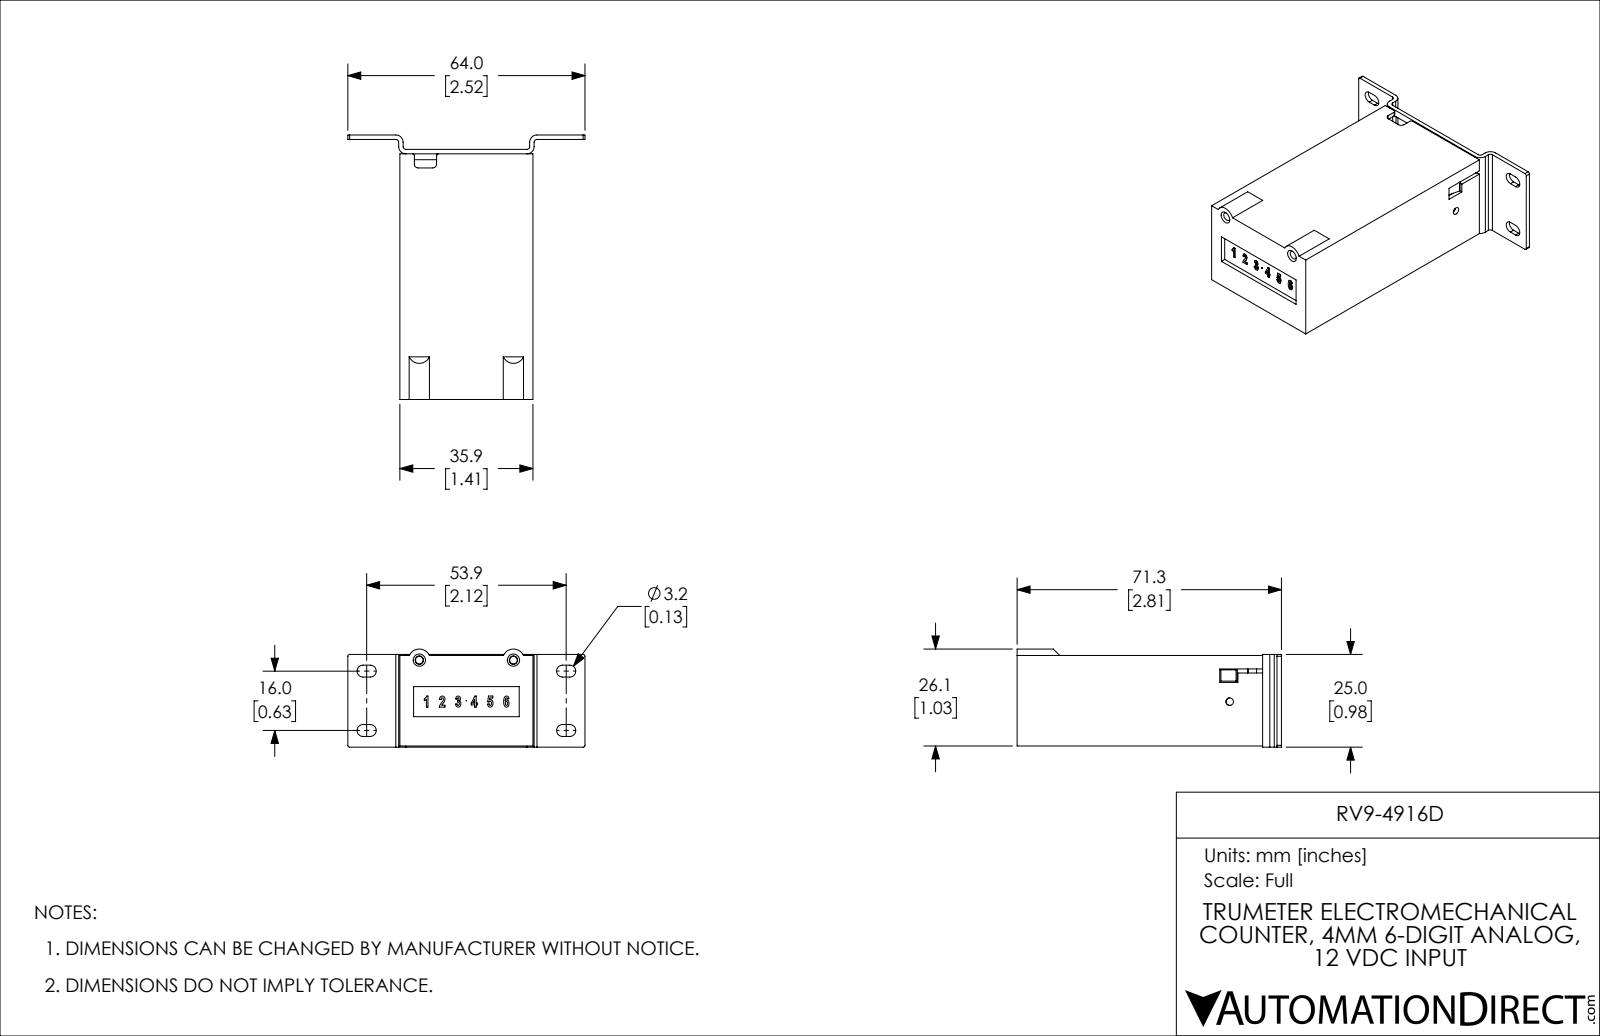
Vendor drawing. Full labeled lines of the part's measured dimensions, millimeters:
Part name (STEP PRODUCT): RV9-4916D
STEP written by: SolidWorks 2021 (CONFIG_CONTROL_DESIGN)
Units: millimetres
Bodies: 1 solid, 354 faces (219 planar, 104 cylindrical, 31 other)
Overall size (bounding box): 71.33 × 64 × 26.46
Volume: 18 281 mm³ · Surface area: 26 612 mm²
Round holes (diameter × count): ⌀2.02 ×5, ⌀3.17 ×2, ⌀4 ×2, ⌀2.01 ×1, ⌀2.03 ×1, ⌀2.46 ×1, ⌀2.46 ×1, ⌀3.12 ×1, ⌀5.6 ×1
Round bosses / shafts (diameter × count): ⌀6 ×2
Partial cylindrical surfaces — rounded edges, fillets, slot ends (radius × count): R0.5 ×11, R1 ×10, R1.6 ×8, R0.75 ×4, R1.95 ×4, R0.25 ×2, R0.3 ×2, R1.5 ×2
Main face-to-face distances: 1.6, 1.35, 34.55, 2.95, 32.95, 31.6, 24.39, 35.9, 33.2, 30
Hole centre spacings: 13.21, 25.86, 26.65, 26.67, 4.75, 5, 7.03, 8.14
